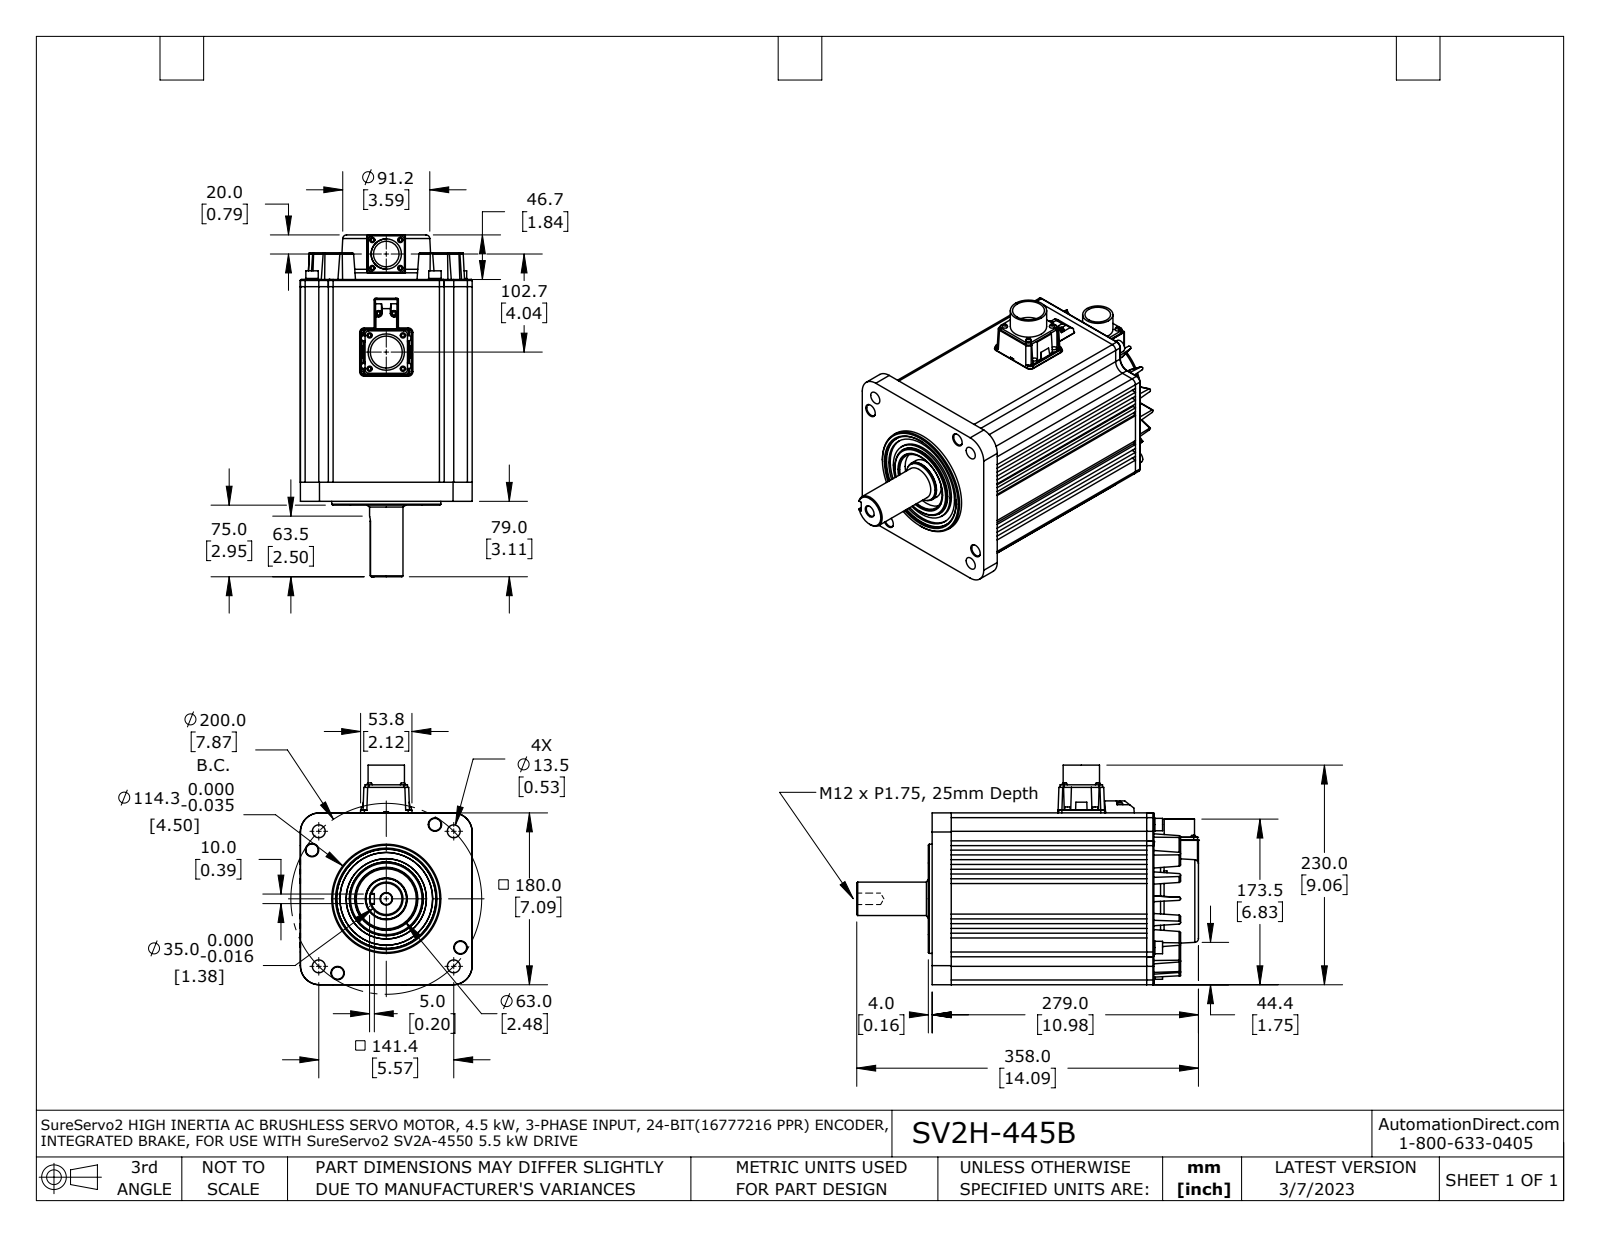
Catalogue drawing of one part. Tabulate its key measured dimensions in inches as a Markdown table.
| quantity | value |
| --- | --- |
| part name | SV2H-x45B |
| STEP written by | SolidWorks 2021 (AUTOMOTIVE_DESIGN) |
| units | inches |
| bodies | 1 solid, 635 faces (336 planar, 204 cylindrical, 95 other) |
| overall size | 14.095 × 9.056 × 7.087 |
| volume | 442.2 in³ |
| surface area | 556.7 in² |
| round holes (diameter × count) | 0.531 × 4, 0.551 × 4, 0.472 × 1, 1.058 × 1, 1.317 × 1, 2.48 × 1 |
| round bosses / shafts (diameter × count) | 0.217 × 7, 0.528 × 4, 0.512 × 4, 0.315 × 4, 0.236 × 2, 4.567 × 1, 4.5 × 1, 1.732 × 1 |
| partial cylindrical surfaces (radius × count) | 0.197 × 17, 0.064 × 16, 0.157 × 16, 0.039 × 12, 0.02 × 4, 0.191 × 4, 0.394 × 4, 0.787 × 4 |
| main face-to-face distances | 0.197, 7.087, 0.394, 1.154, 5.933, 0.591, 3.031, 3.228, 2.835, 0.787 |
| hole center spacings | 0.824, 3.661, 3.937, 4.8, 5.178, 5.568, 5.897, 7.559 |
